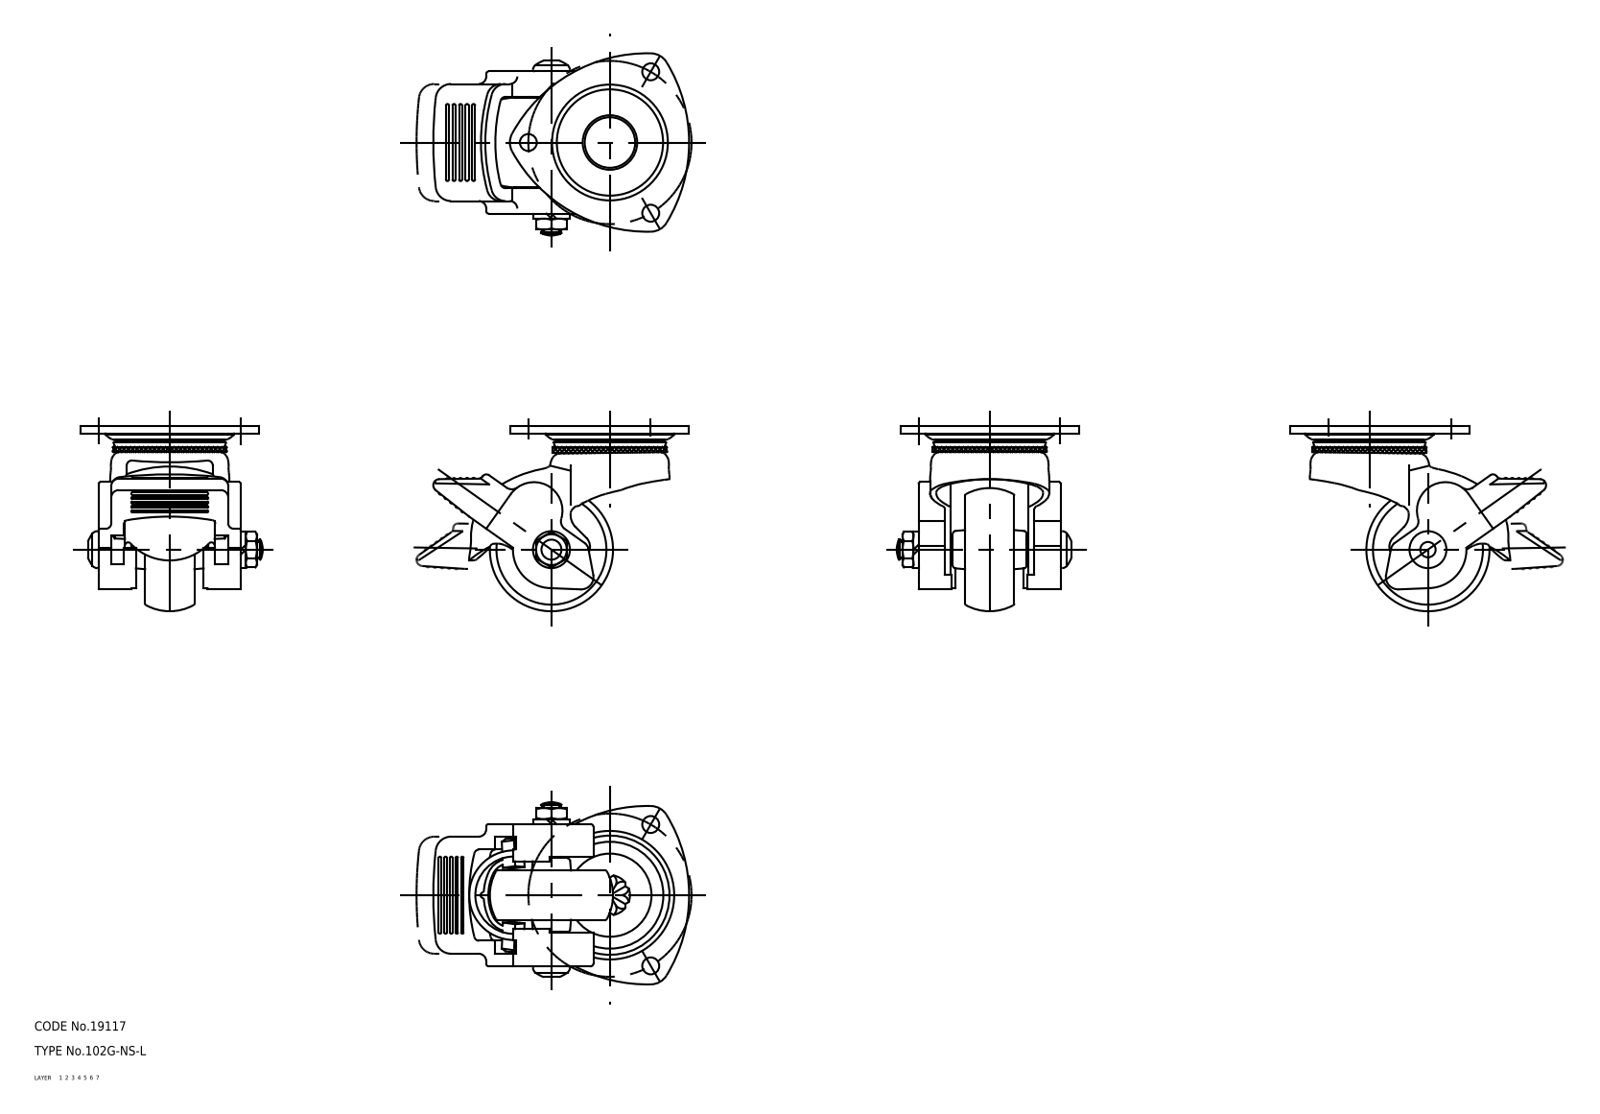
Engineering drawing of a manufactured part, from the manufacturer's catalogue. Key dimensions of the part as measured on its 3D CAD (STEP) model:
Part name (STEP PRODUCT): lever; wheel; mounting plate; main shaft (+2 more)
STEP written by: CADfix (AUTOMOTIVE_DESIGN)
Units: millimetres
Bodies: 6 solids, 400 faces (0 planar, 0 cylindrical, 400 other)
Overall size (bounding box): 83.07 × 60 × 59.16
Volume: 59 114 mm³ · Surface area: 32 180 mm²
